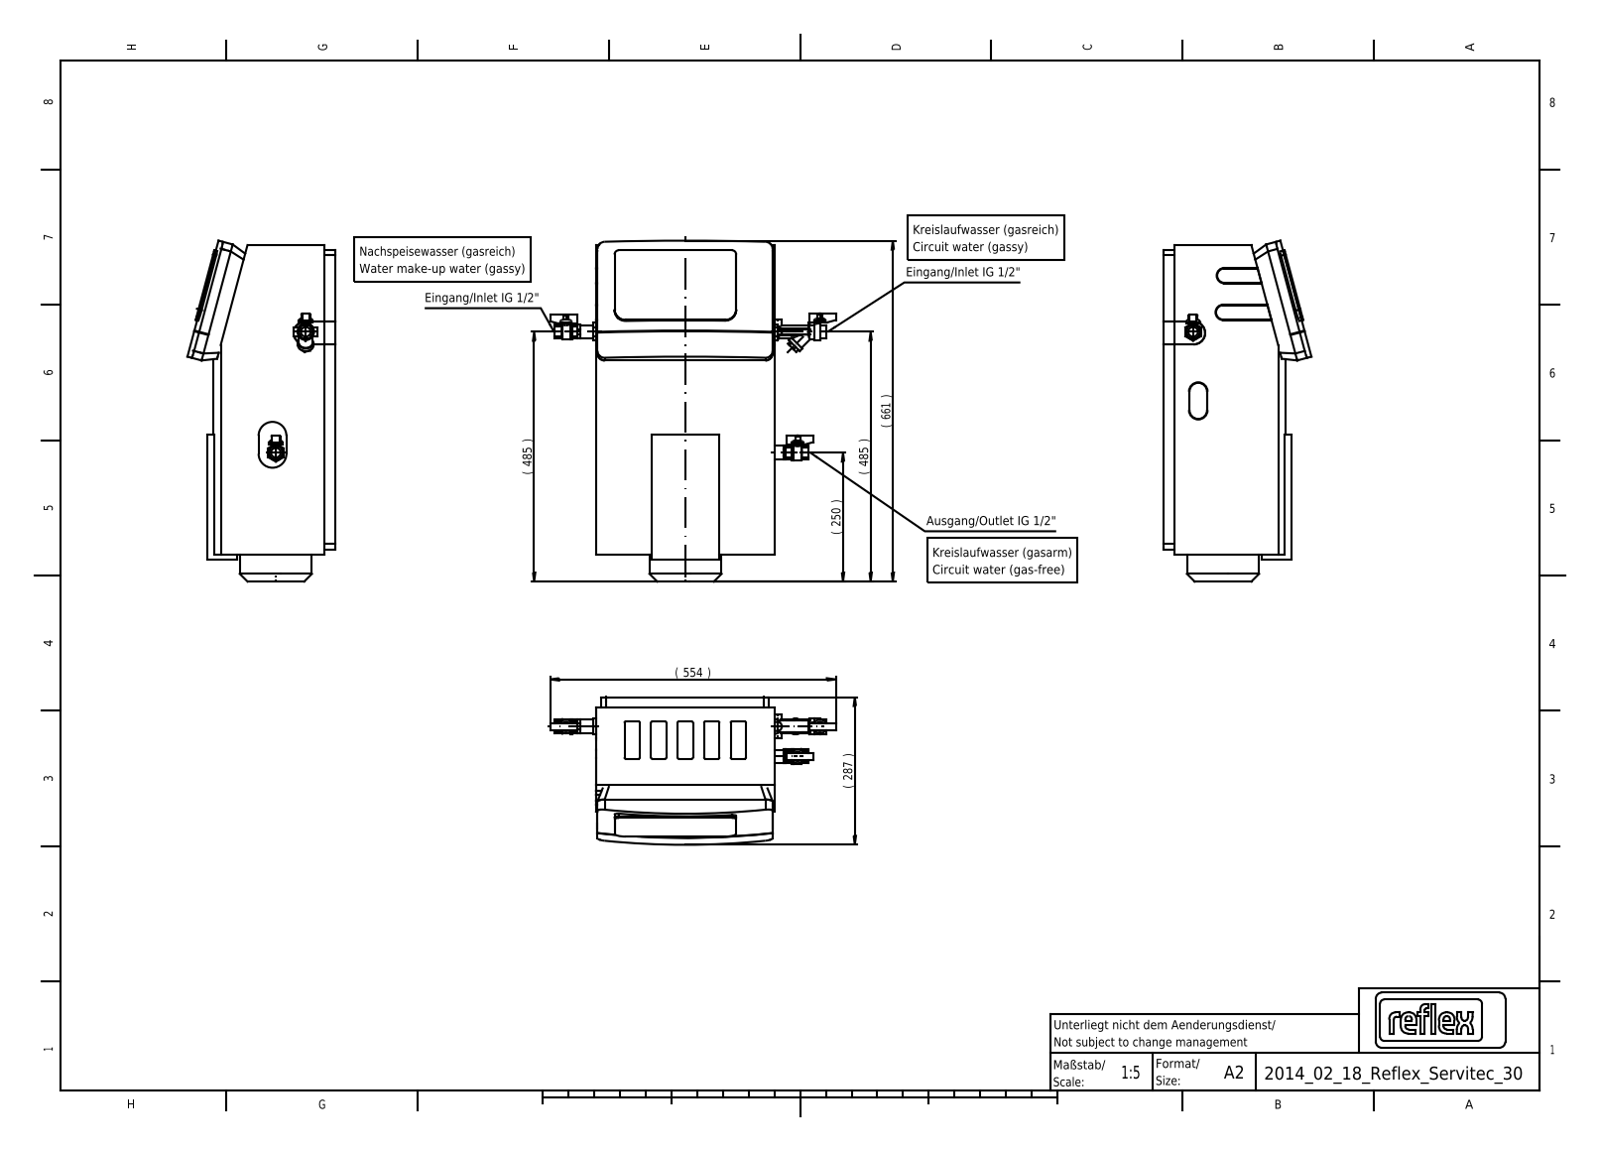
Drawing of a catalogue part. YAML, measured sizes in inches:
step_written_by: "Mechanical Desktop 2011 (CONFIG_CONTROL_DESIGN)"
units: inches
bodies: {solids: 41, faces: 1956, planar: 971, cylindrical: 448, other: 537}
overall_size: [26.037, 21.824, 11.283]
volume: 3533
surface_area: 2926
round_holes:
  - {diameter: 0.413, count: 7}
  - {diameter: 0.24, count: 4}
  - {diameter: 0.736, count: 2}
  - {diameter: 0.157, count: 1}
  - {diameter: 0.669, count: 1}
  - {diameter: 0.787, count: 1}
  - {diameter: 5.276, count: 1}
round_bosses_or_shafts:
  - {diameter: 0.63, count: 9}
  - {diameter: 0.748, count: 7}
  - {diameter: 0.689, count: 7}
  - {diameter: 1.181, count: 5}
  - {diameter: 0.315, count: 5}
  - {diameter: 1.024, count: 4}
  - {diameter: 0.709, count: 4}
  - {diameter: 0.458, count: 4}
partial_cylinders:
  - {radius: 0.02, count: 56}
  - {radius: 0.394, count: 24}
  - {radius: 0.118, count: 20}
  - {radius: 0.197, count: 19}
  - {radius: 4.134, count: 10}
  - {radius: 0.039, count: 8}
  - {radius: 0.551, count: 6}
  - {radius: 4.063, count: 5}
face_to_face_distances: [5.996, 23.622, 17.626, 0.394, 2.934, 12.163, 6.167, 11.459, 23.228, 17.232]
hole_center_spacings: [1.417, 2.835, 4.252, 1.063, 5.669, 1.135, 1.142, 1.556]
